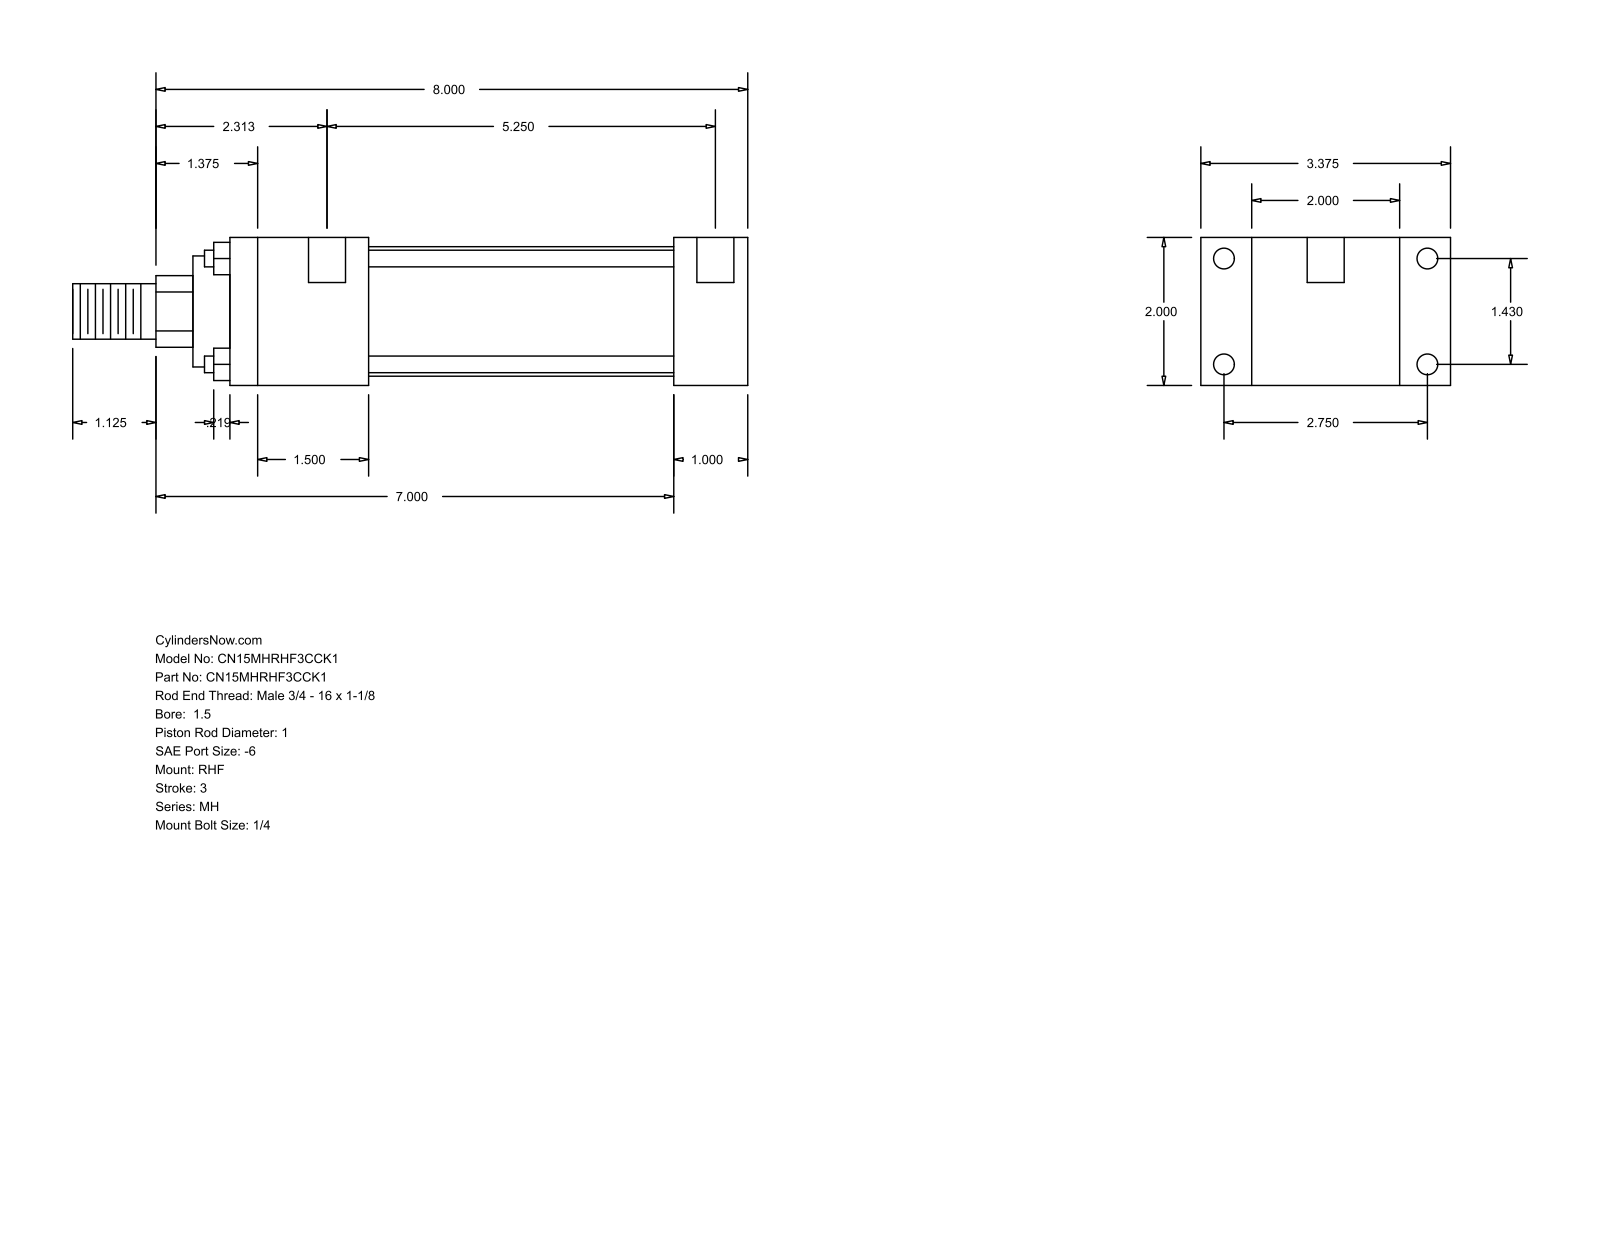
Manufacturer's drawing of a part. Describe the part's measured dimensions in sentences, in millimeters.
The part is named "MH_RHF__0150_1". Its 3-D file was written by "GSSL Pune (CONFIG_CONTROL_DESIGN)". It is 0 solids with 88 faces: 60 planar, 28 cylindrical and 0 other. Overall it measures 231.78 by 85.72 by 50.8 millimeters. Round holes: 4 of diameter 5.56, 4 of diameter 7.14, 2 of diameter 12.7. Round bosses or shafts: 4 of diameter 5.71, 1 of diameter 44.45, 1 of diameter 38.1, 1 of diameter 25.4, 1 of diameter 19.05. Partial cylindrical surfaces (rounded edges, fillets, slot ends): 1 of radius 12.29. The main face-to-face distances are 50.8, 25.4, 17.46, 68.26, 85.72, 177.8, 152.4, 47.63, 104.77, 130.17. The hole center spacings are 36.32, 69.84, 78.72, 136.53, 3.18, 133.35.
